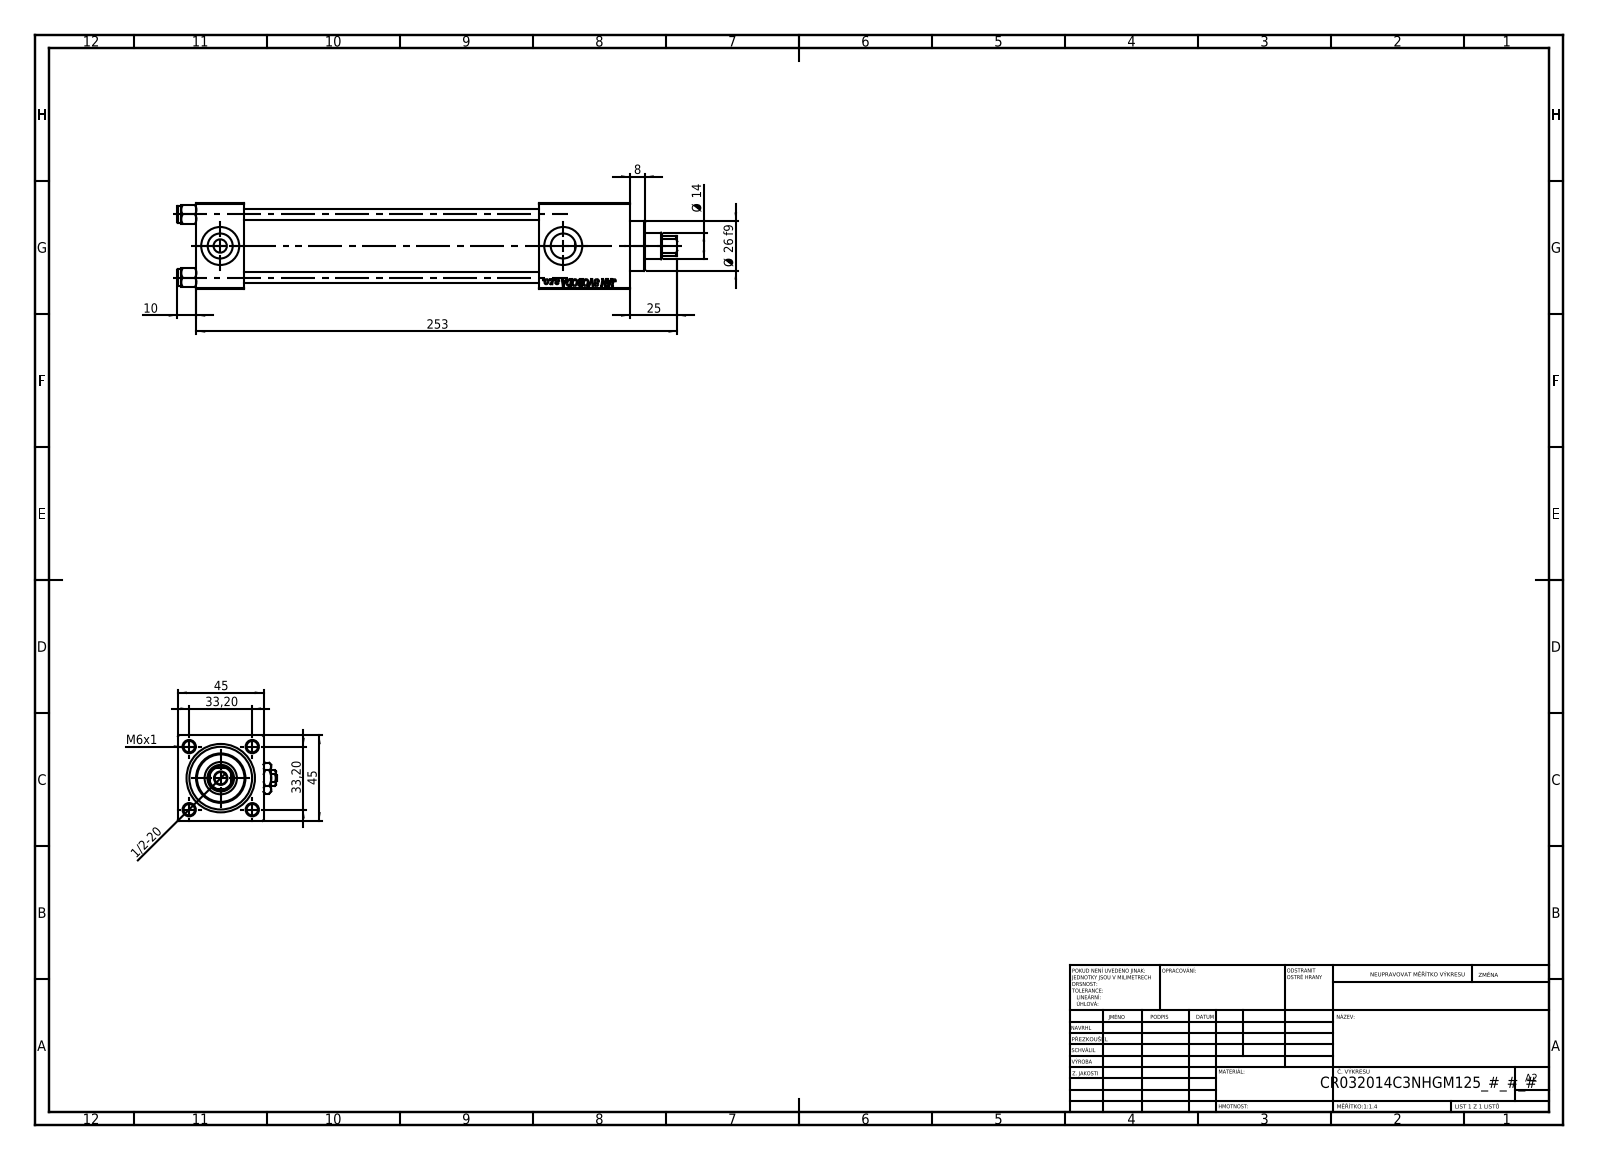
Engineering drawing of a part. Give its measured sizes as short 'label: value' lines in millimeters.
name: V215CR_C_Body; V215CR_VCP_C; Zatka_pro_OIL_PORT; V215CR_C_TYCINKA (+2 more)
written by: SolidWorks 2019 (CONFIG_CONTROL_DESIGN)
unit: mm
bodies: 13 solids, 1248 faces (572 planar, 98 cylindrical, 578 other)
size: 263 × 52 × 45
volume: 255 017 mm³; area: 104 551 mm²
holes: 4× ⌀6, 2× ⌀7, 2× ⌀13.16, 2× ⌀20, 1× ⌀6.5, 1× ⌀14, 1× ⌀17, 1× ⌀24, 1× ⌀32, 1× ⌀33
bosses: 4× ⌀9, 1× ⌀38, 1× ⌀26
rounds: 1× R6.5
face distances: 45, 25, 203, 228, 180, 155, 48, 199.3, 174.3, 19.3
hole spacings: 23.48, 33.2, 46.95, 180.5
